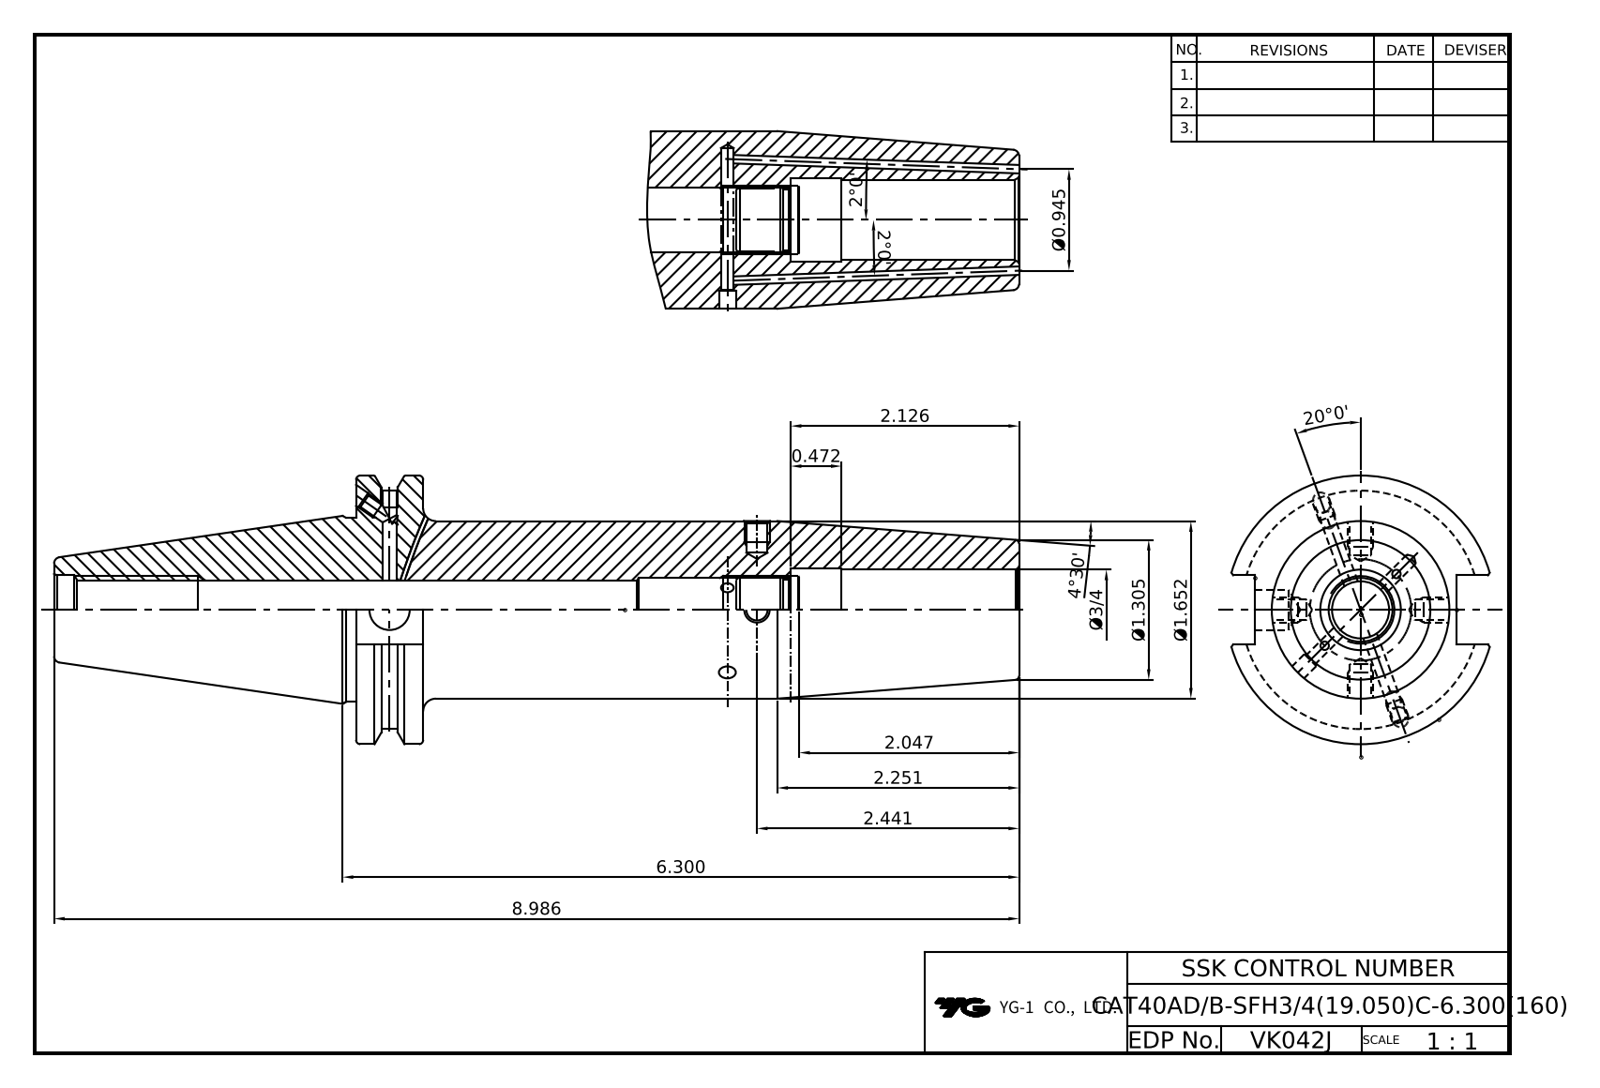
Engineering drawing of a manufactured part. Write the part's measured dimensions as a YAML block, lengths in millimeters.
part_name: "LO-CAT40ADB-SFH19.05C-160"
step_written_by: "Autodesk Inventor 2022 (AUTOMOTIVE_DESIGN)"
units: millimeters
bodies: {solids: 1, faces: 91, planar: 37, cylindrical: 31, other: 23}
overall_size: [228.25, 63.5, 61.09]
volume: 251419
surface_area: 45581
round_holes:
  - {diameter: 3.24, count: 4}
  - {diameter: 2.5, count: 2}
  - {diameter: 4, count: 2}
  - {diameter: 4.2, count: 2}
  - {diameter: 9.53, count: 1}
  - {diameter: 13, count: 1}
  - {diameter: 13.39, count: 1}
  - {diameter: 14.92, count: 1}
  - {diameter: 16.3, count: 1}
  - {diameter: 19.05, count: 1}
  - {diameter: 20.25, count: 1}
round_bosses_or_shafts:
  - {diameter: 63.5, count: 1}
  - {diameter: 43.6, count: 1}
  - {diameter: 42, count: 1}
partial_cylinders:
  - {radius: 28.15, count: 1}
face_to_face_distances: [15.88, 156.83, 140.95, 47.6, 16.38, 102.83, 86.95, 54, 71.42, 87.3]
